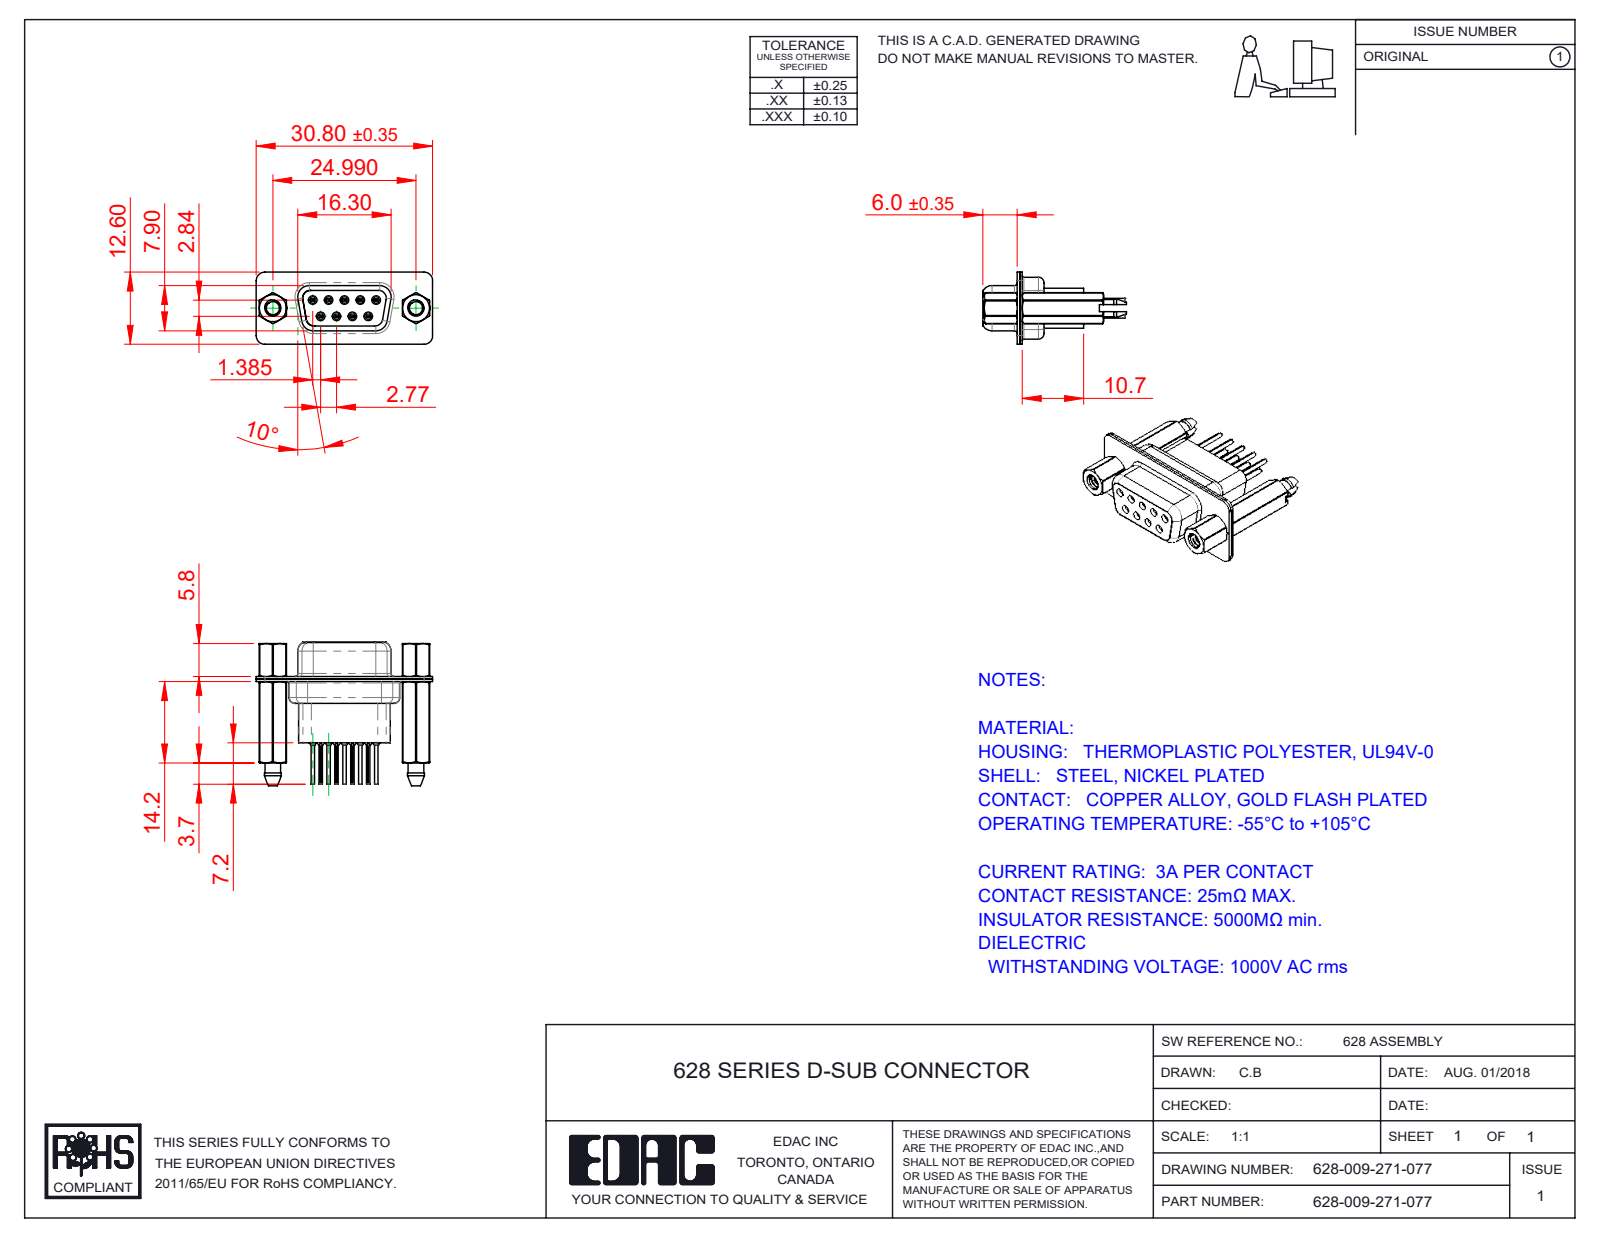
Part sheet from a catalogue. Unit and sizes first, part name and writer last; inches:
Units: inches
Overall size (bounding box): 1.213 × 0.988 × 0.496
Round holes (diameter × count): ⌀0.008 ×9, ⌀0.031 ×9, ⌀0.035 ×9, ⌀0.043 ×9, ⌀0.063 ×9, ⌀0.067 ×5, ⌀0.089 ×2, ⌀0.09 ×2, ⌀0.157 ×2, ⌀0.159 ×2, ⌀0.191 ×2
Round bosses / shafts (diameter × count): ⌀0.079 ×9, ⌀0.059 ×9, ⌀0.047 ×9, ⌀0.024 ×9, ⌀0.195 ×2, ⌀0.189 ×2, ⌀0.11 ×2
Partial cylindrical surfaces — rounded edges, fillets, slot ends (radius × count): R0.059 ×19, R0.004 ×18, R0.079 ×12, R0.011 ×9, R0.053 ×6, R0.063 ×6, R0.01 ×4, R0.02 ×4
Main face-to-face distances: 0.018, 0.016, 0.035, 0.187, 0.335, 0.26, 0.075, 0.055, 0.276, 0.02
Hole centre spacings: 0.124, 0.109, 0.218, 0.198, 0.198, 0.327, 0.294, 0.295
Volume: 0.172 in³ · Surface area: 10.18 in²
Bodies: 16 solids, 1586 faces (400 planar, 538 cylindrical, 648 other)
Part name (STEP PRODUCT): 628 Housing_09 HP; 628 Contact Row 2_71; 628 Contact Row 1_71; 628 Shell Rear_09 Contacts (+4 more)
STEP written by: SolidWorks 2020 (CONFIG_CONTROL_DESIGN)
